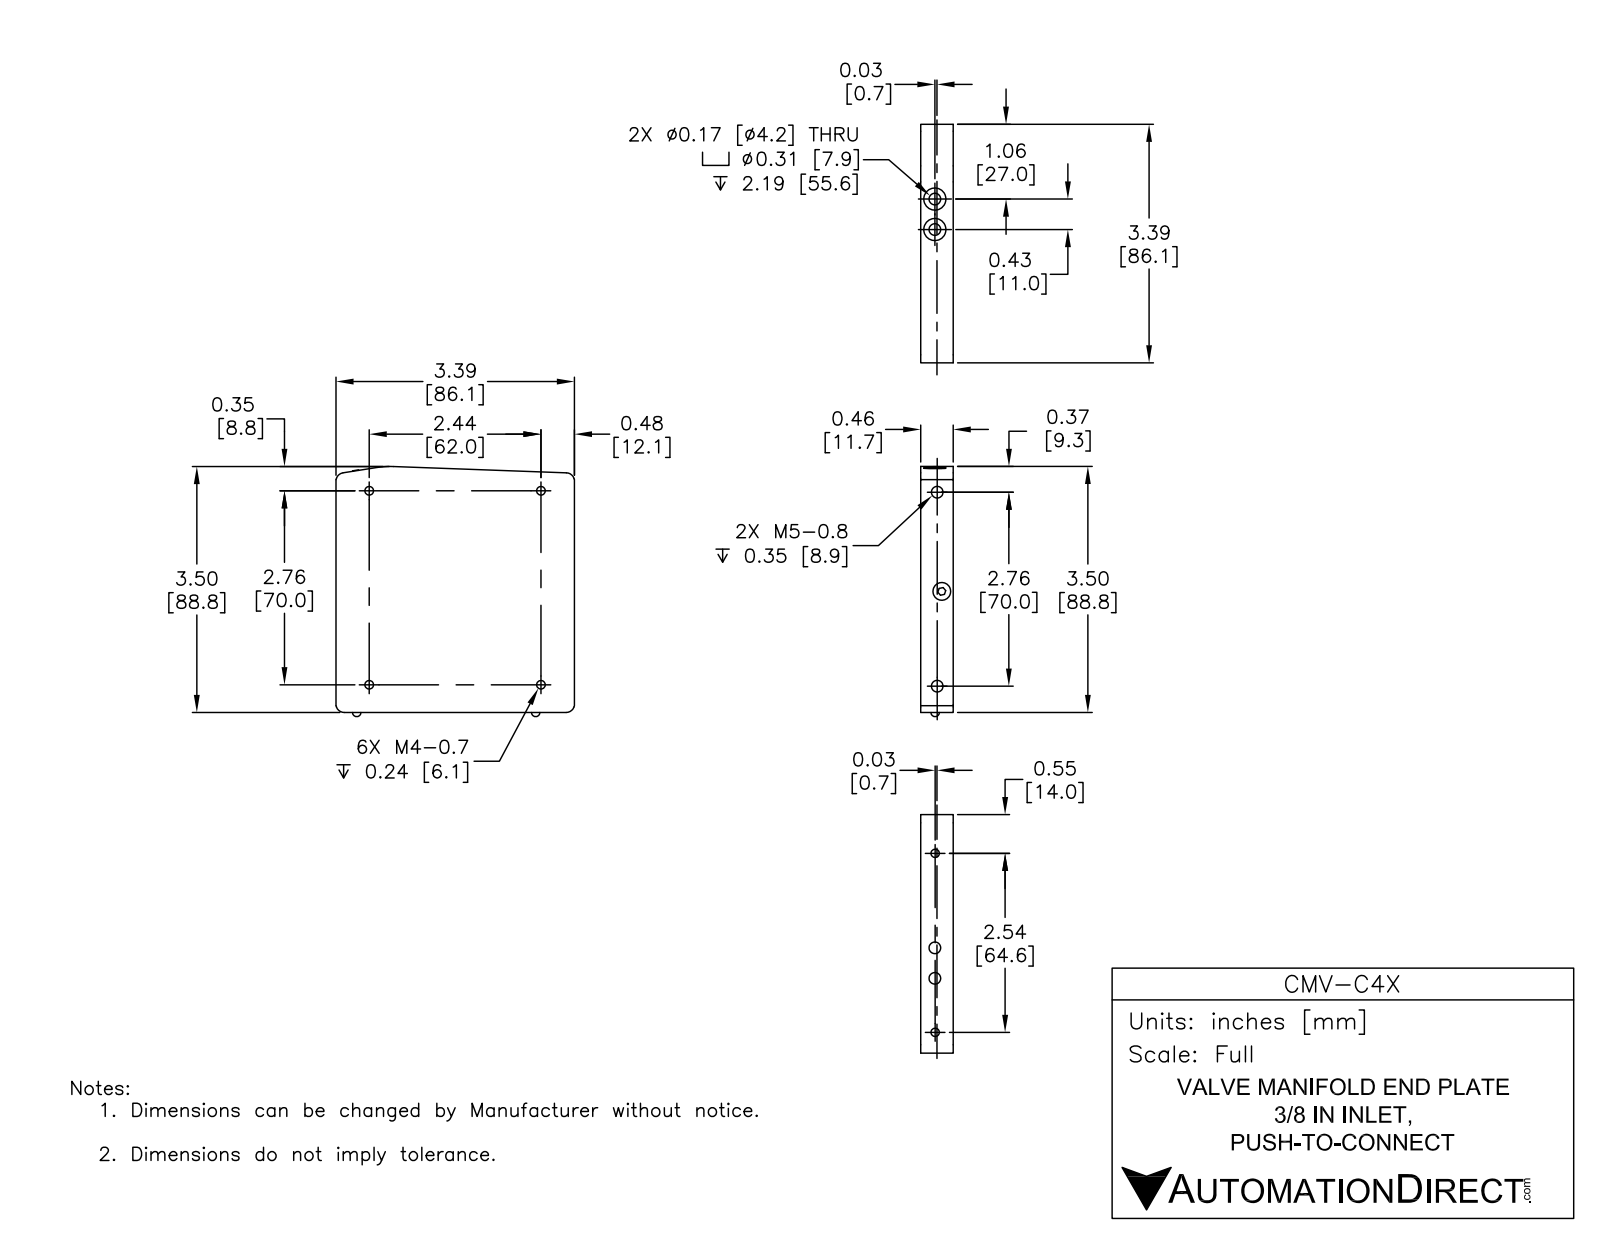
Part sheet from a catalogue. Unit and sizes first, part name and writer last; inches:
Units: inches
Overall size (bounding box): 3.545 × 3.39 × 0.465
Round holes (diameter × count): ⌀0.157 ×6, ⌀0.256 ×2, ⌀0.315 ×2, ⌀0.246 ×1, ⌀0.252 ×1
Partial cylindrical surfaces — rounded edges, fillets, slot ends (radius × count): R0.063 ×4, R0.118 ×4, R0.189 ×4, R1.181 ×1
Main face-to-face distances: 0.465, 0.431, 0.033, 3.39, 3.232, 0.157, 1.339, 0.276, 0.189, 0.242
Hole centre spacings: 0.433, 0.837, 1.27, 1.303, 1.329, 1.431, 1.457, 1.736
Volume: 4.861 in³ · Surface area: 37.97 in²
Bodies: 12 solids, 194 faces (136 planar, 32 cylindrical, 26 other)
Part name (STEP PRODUCT): CMV-C4X
STEP written by: SolidWorks 2013 (AUTOMOTIVE_DESIGN)
